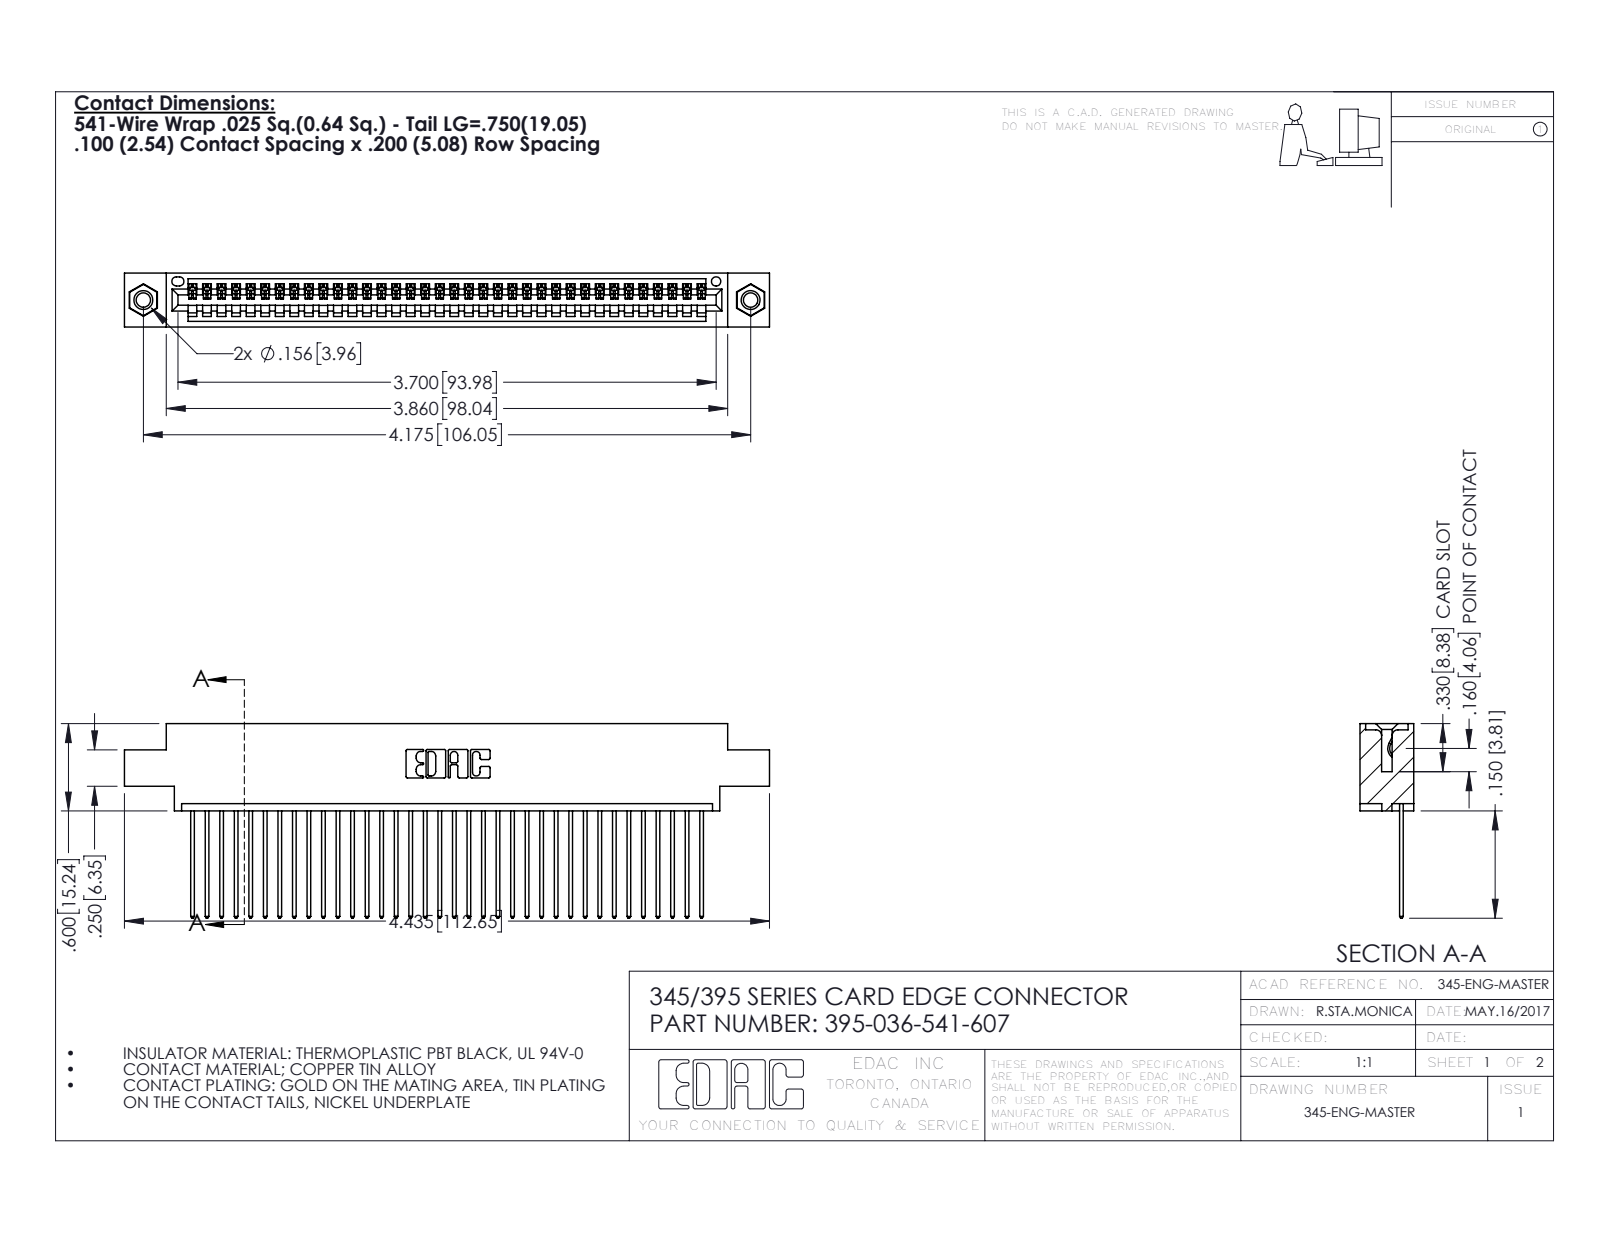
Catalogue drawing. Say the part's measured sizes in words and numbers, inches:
The part is named "345 Part_0.170 Offset - 0.156 Dia-TI; 395-036-541-607; 345-250-001_345-250-005-103; 345-292-001_345-293-141". Its 3-D file was written by "SolidWorks 2016 (CONFIG_CONTROL_DESIGN)". It is 39 solids with 2278 faces: 1556 planar, 706 cylindrical and 16 other. Overall it measures 4.435 by 1.337 by 0.37 inches. Its volume is 0.649 cubic inches and its surface area 23.12 square inches. Round holes: 2 of diameter 0.098, 2 of diameter 0.125, 2 of diameter 0.156, 1 of diameter 0.064. Round bosses or shafts: 2 of diameter 0.155. Partial cylindrical surfaces (rounded edges, fillets, slot ends): 72 of radius 0.006, 72 of radius 0.01, 22 of radius 0.01, 6 of radius 0.007, 6 of radius 0.031, 3 of radius 0.026, 2 of radius 0.031, 2 of radius 0.04. The main face-to-face distances are 0.072, 0.298, 0.37, 0.098, 0.272, 0.025, 0.2, 0.225, 0.175, 0.149. The hole center spacings are 0.27, 3.939, 4.175.
